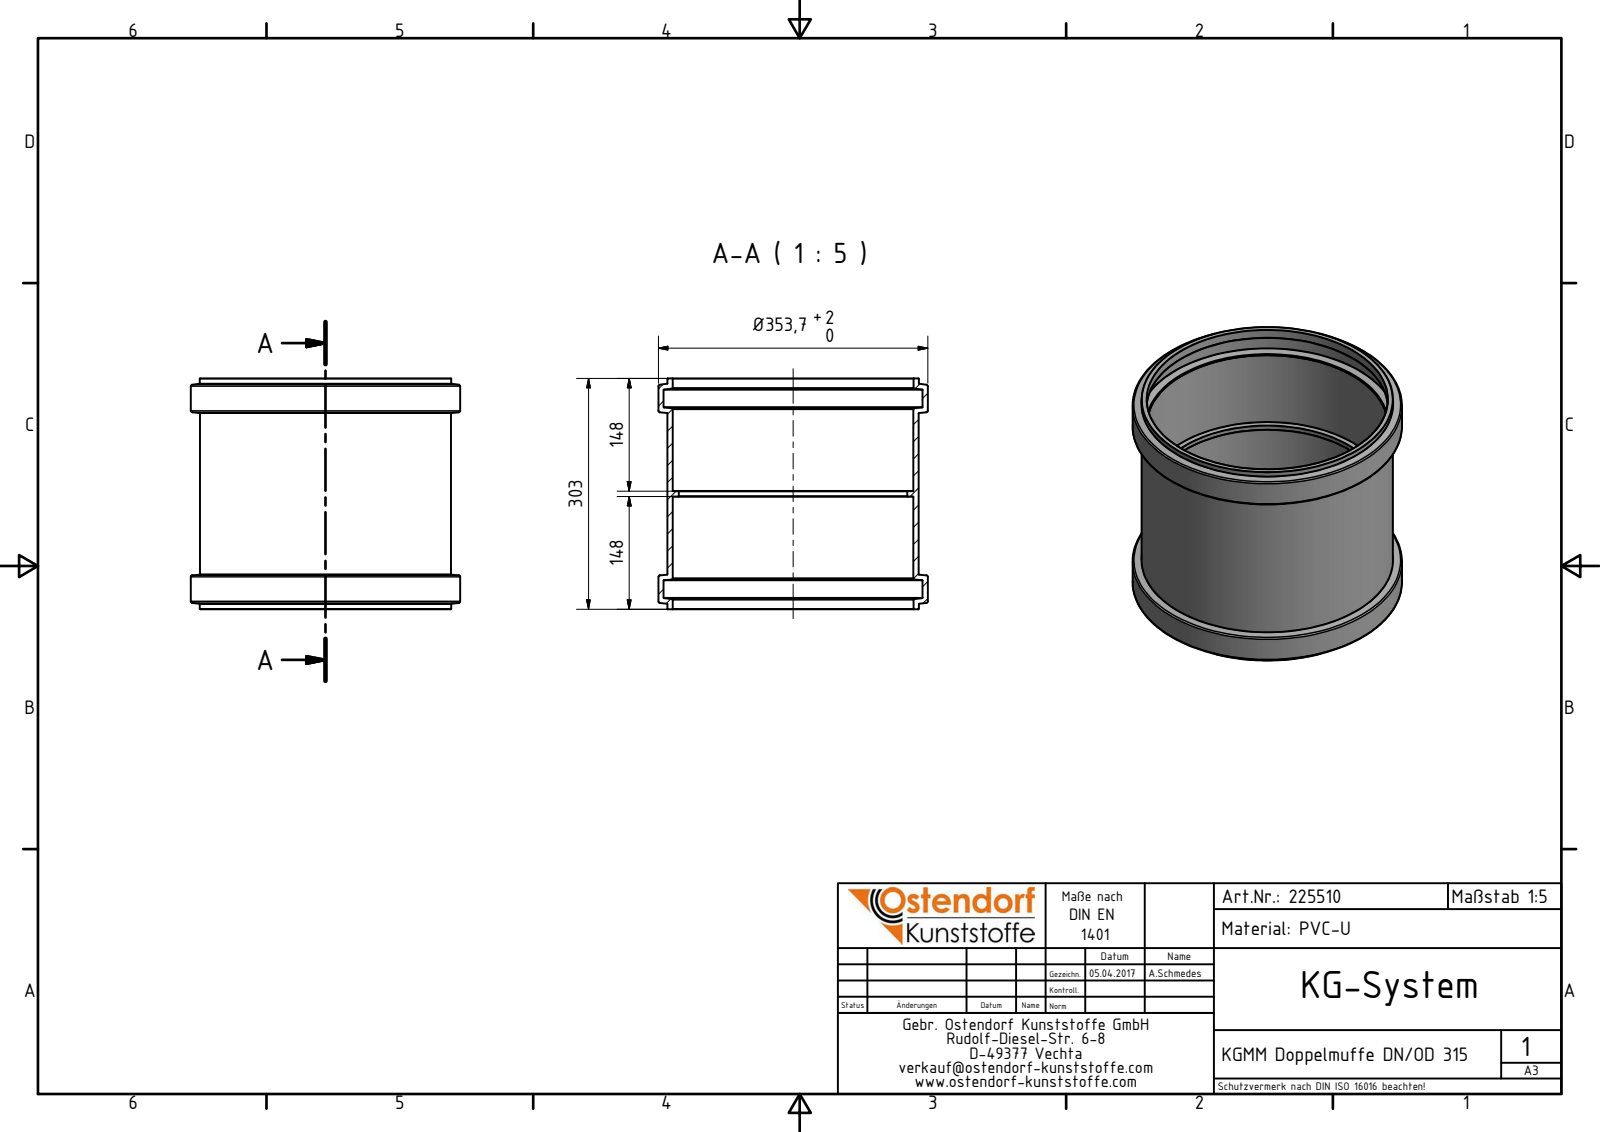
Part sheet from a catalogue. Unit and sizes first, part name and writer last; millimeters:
Units: millimetres
Overall size (bounding box): 353.7 × 353.7 × 303
Round holes (diameter × count): ⌀300 ×1, ⌀316 ×1, ⌀316.3 ×1, ⌀339.9 ×1
Round bosses / shafts (diameter × count): ⌀353.7 ×1, ⌀330.1 ×1, ⌀329.8 ×1
Main face-to-face distances: 148, 155, 7, 303, 40.55, 262.45, 107.45, 114.45, 221.9
Volume: 2 514 000 mm³ · Surface area: 735 819 mm²
Bodies: 1 solid, 52 faces (6 planar, 14 cylindrical, 32 other)
Part name (STEP PRODUCT): 225510 KGMM Doppelmuffe DN_OD 315
STEP written by: Autodesk Inventor 2016 (AUTOMOTIVE_DESIGN)
